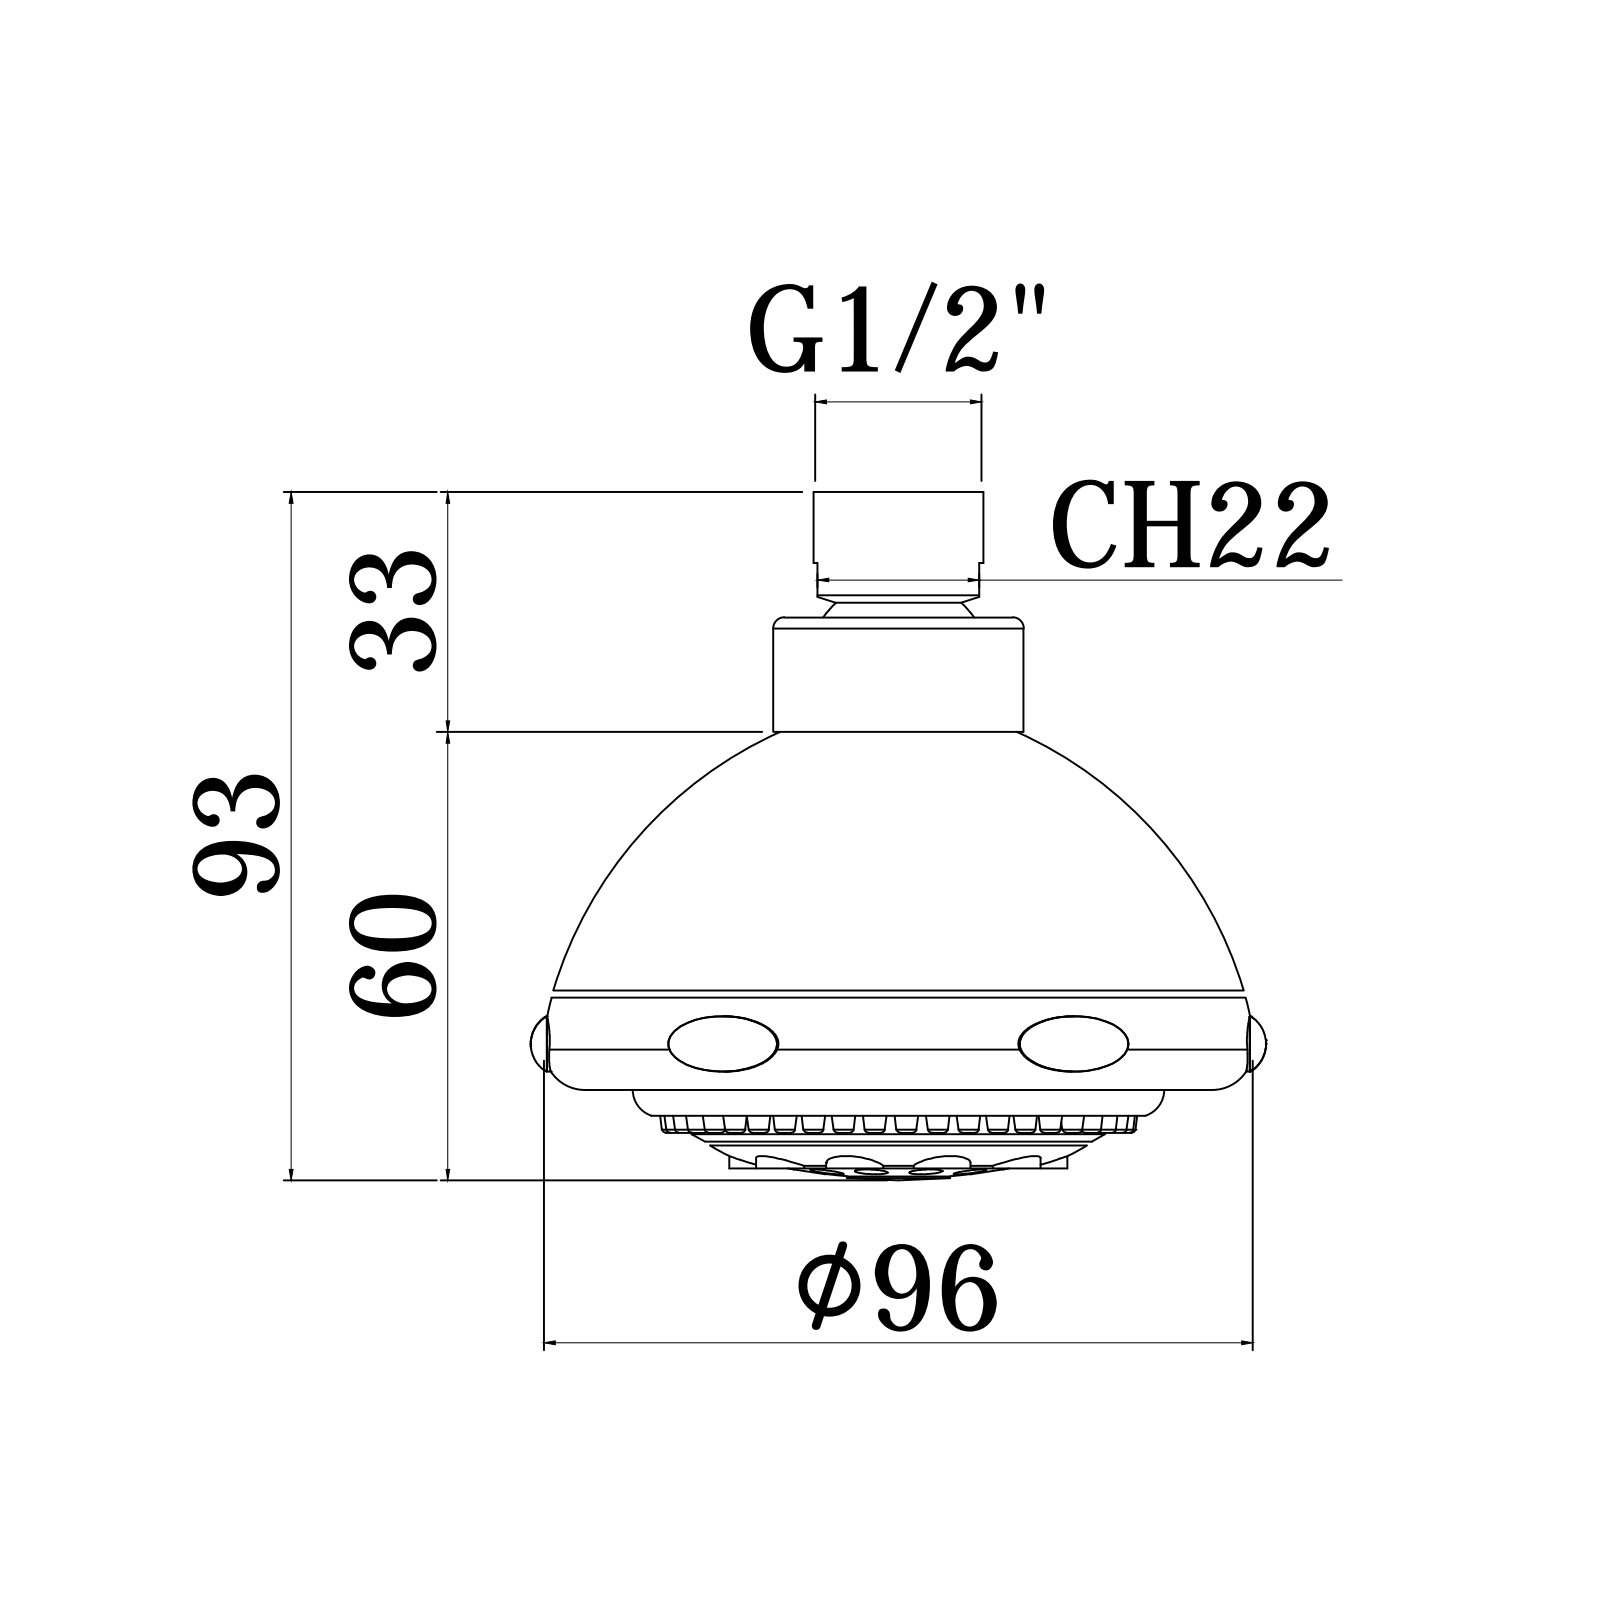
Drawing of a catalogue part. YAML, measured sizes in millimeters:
part_name: "4071302CR"
step_written_by: "CREO PARAMETRIC BY PTC INC, 2020044 (CONFIG_CONTROL_DESIGN)"
units: millimeters
bodies: {solids: 3, faces: 5914, planar: 4031, cylindrical: 1335, other: 548}
overall_size: [99.1, 96.7, 96.2]
volume: 7140
surface_area: 94260
round_holes:
  - {diameter: 1.7, count: 10}
  - {diameter: 4.2, count: 10}
  - {diameter: 4.8, count: 10}
  - {diameter: 3.5, count: 1}
  - {diameter: 4, count: 1}
  - {diameter: 6.8, count: 1}
  - {diameter: 12.2, count: 1}
  - {diameter: 13.9, count: 1}
  - {diameter: 14.5, count: 1}
  - {diameter: 18.6, count: 1}
  - {diameter: 19.1, count: 1}
  - {diameter: 21, count: 1}
round_bosses_or_shafts:
  - {diameter: 3.4, count: 40}
  - {diameter: 91.5, count: 1}
  - {diameter: 86.2, count: 1}
  - {diameter: 85.2, count: 1}
  - {diameter: 75.2, count: 1}
  - {diameter: 72.3, count: 1}
  - {diameter: 71, count: 1}
  - {diameter: 69.6, count: 1}
partial_cylinders:
  - {radius: 1, count: 24}
  - {radius: 4, count: 10}
  - {radius: 2.6, count: 8}
  - {radius: 5.7, count: 1}
  - {radius: 10.3, count: 1}
  - {radius: 11, count: 1}
  - {radius: 12, count: 1}
  - {radius: 14.1, count: 1}
face_to_face_distances: [2.5, 8.4, 11, 1.8, 15.3, 5.6, 15.6, 11.3, 4.9, 10.7]
hole_center_spacings: [12, 28.7, 18.8, 24.7, 8, 11, 17.8, 19]
